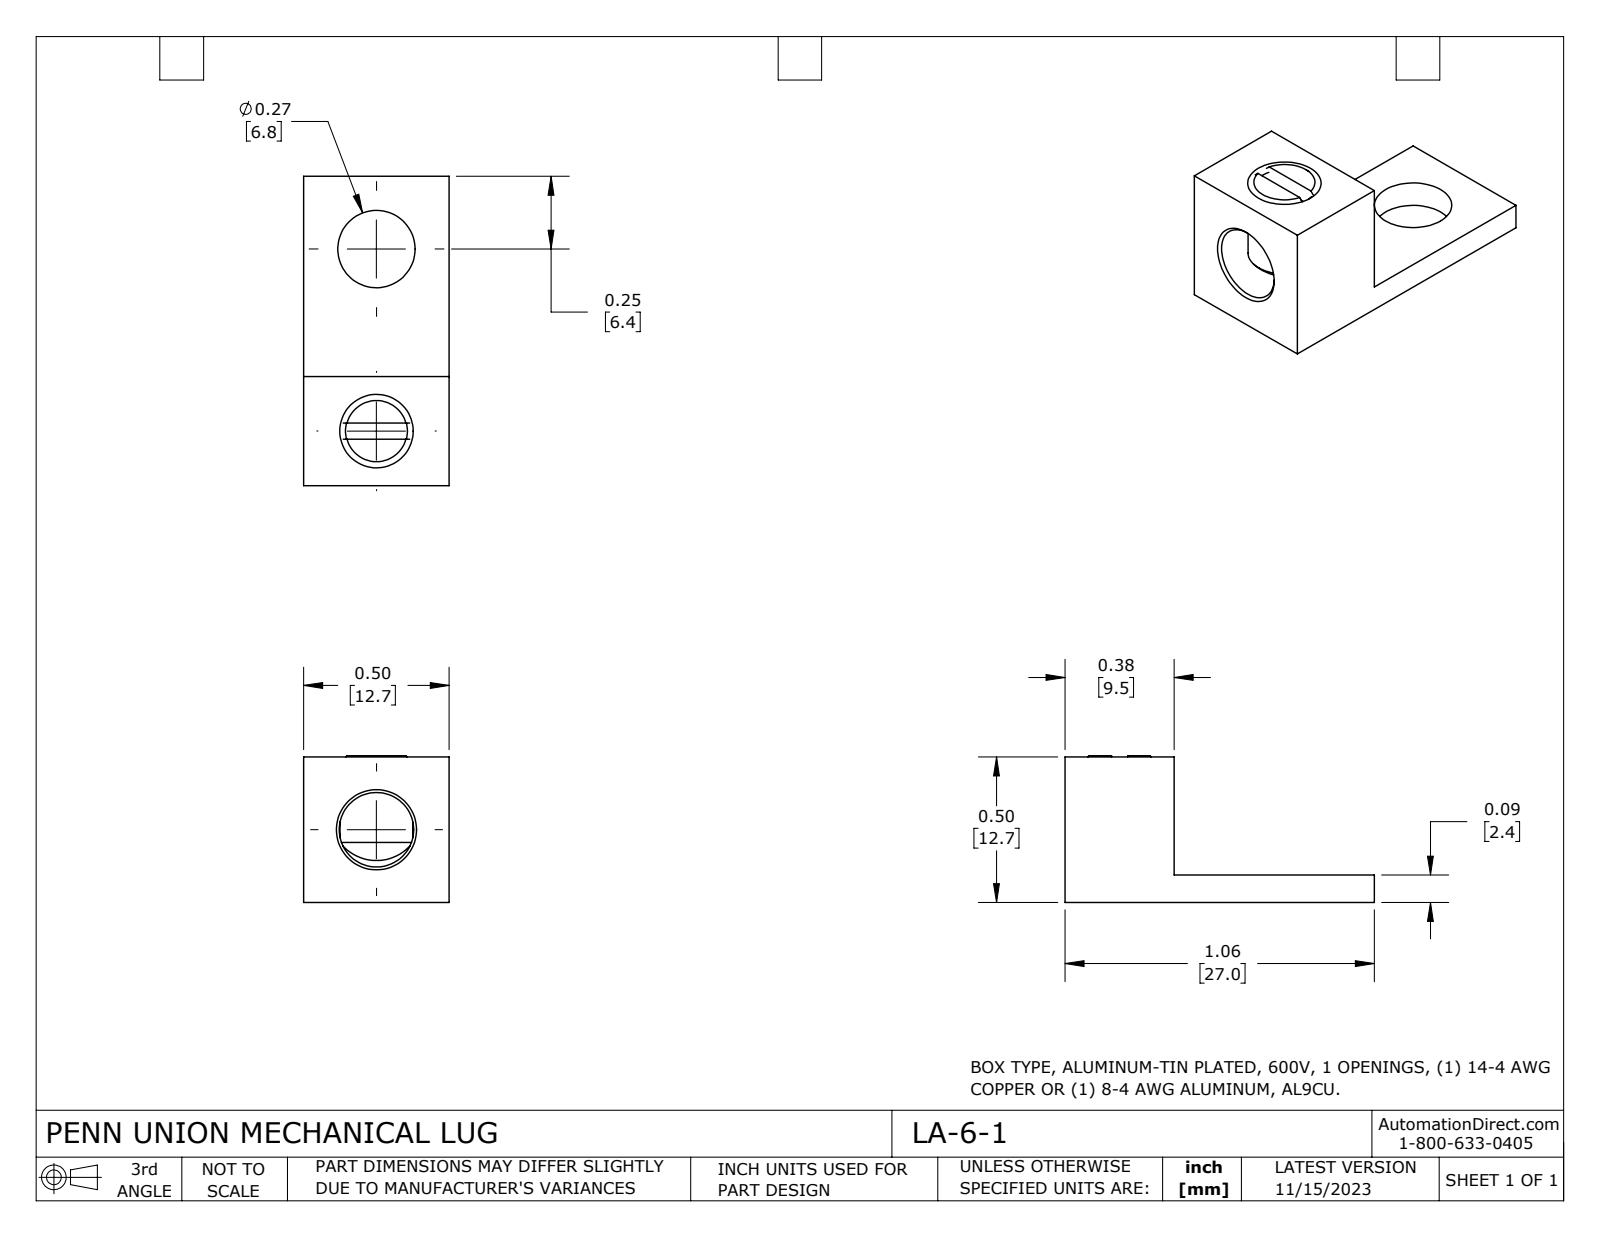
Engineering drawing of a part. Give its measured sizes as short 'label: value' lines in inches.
name: LA-6-1
written by: SolidWorks 2023 (CONFIG_CONTROL_DESIGN)
unit: in
bodies: 2 solids, 30 faces (13 planar, 8 cylindrical, 9 other)
size: 1.063 × 0.504 × 0.5
volume: 0.112 in³; area: 2.605 in²
holes: 1× ⌀0.213, 1× ⌀0.256, 1× ⌀0.266
bosses: 1× ⌀0.25
face distances: 0.5, 0.094, 0.375, 0.406, 1.063, 0.688, 0.16, 0.215, 0.504, 0.41
hole spacings: 0.626
